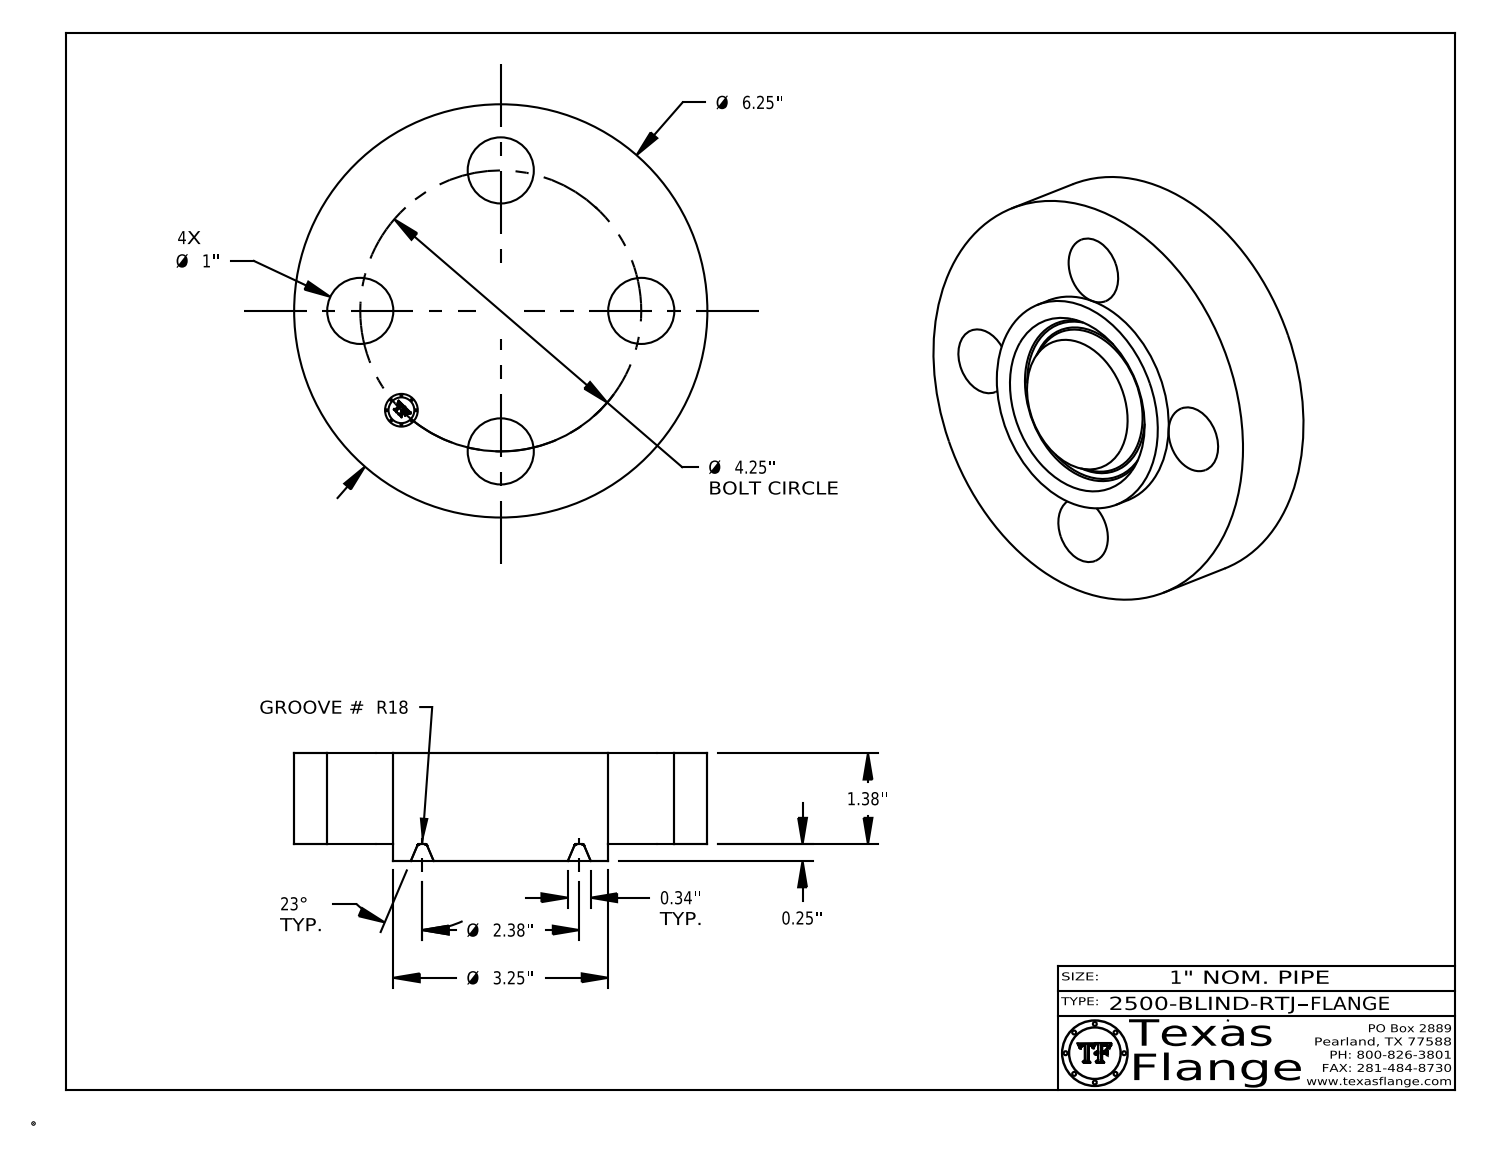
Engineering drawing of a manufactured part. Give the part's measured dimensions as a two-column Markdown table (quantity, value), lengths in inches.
| quantity | value |
| --- | --- |
| part name | 2500-BLIND-RTJ |
| STEP written by | CATIA V5 STEP AP214 (AUTOMOTIVE_DESIGN) |
| units | inches |
| bodies | 1 solid, 410 faces (370 planar, 32 cylindrical, 8 other) |
| overall size | 6.25 × 6.25 × 1.63 |
| volume | 39.63 in³ |
| surface area | 104.6 in² |
| round holes (diameter × count) | 1 × 4, 0.495 × 1 |
| round bosses / shafts (diameter × count) | 0.03 × 8, 6.25 × 1, 3.25 × 1, 0.39 × 1 |
| main face-to-face distances | 1.38, 0.25, 1.63, 1.615, 1.365, 0.015, 0.148, 0.144, 0.027, 0.096 |
| hole center spacings | 3.006, 1.626, 3.927, 4.25 |
